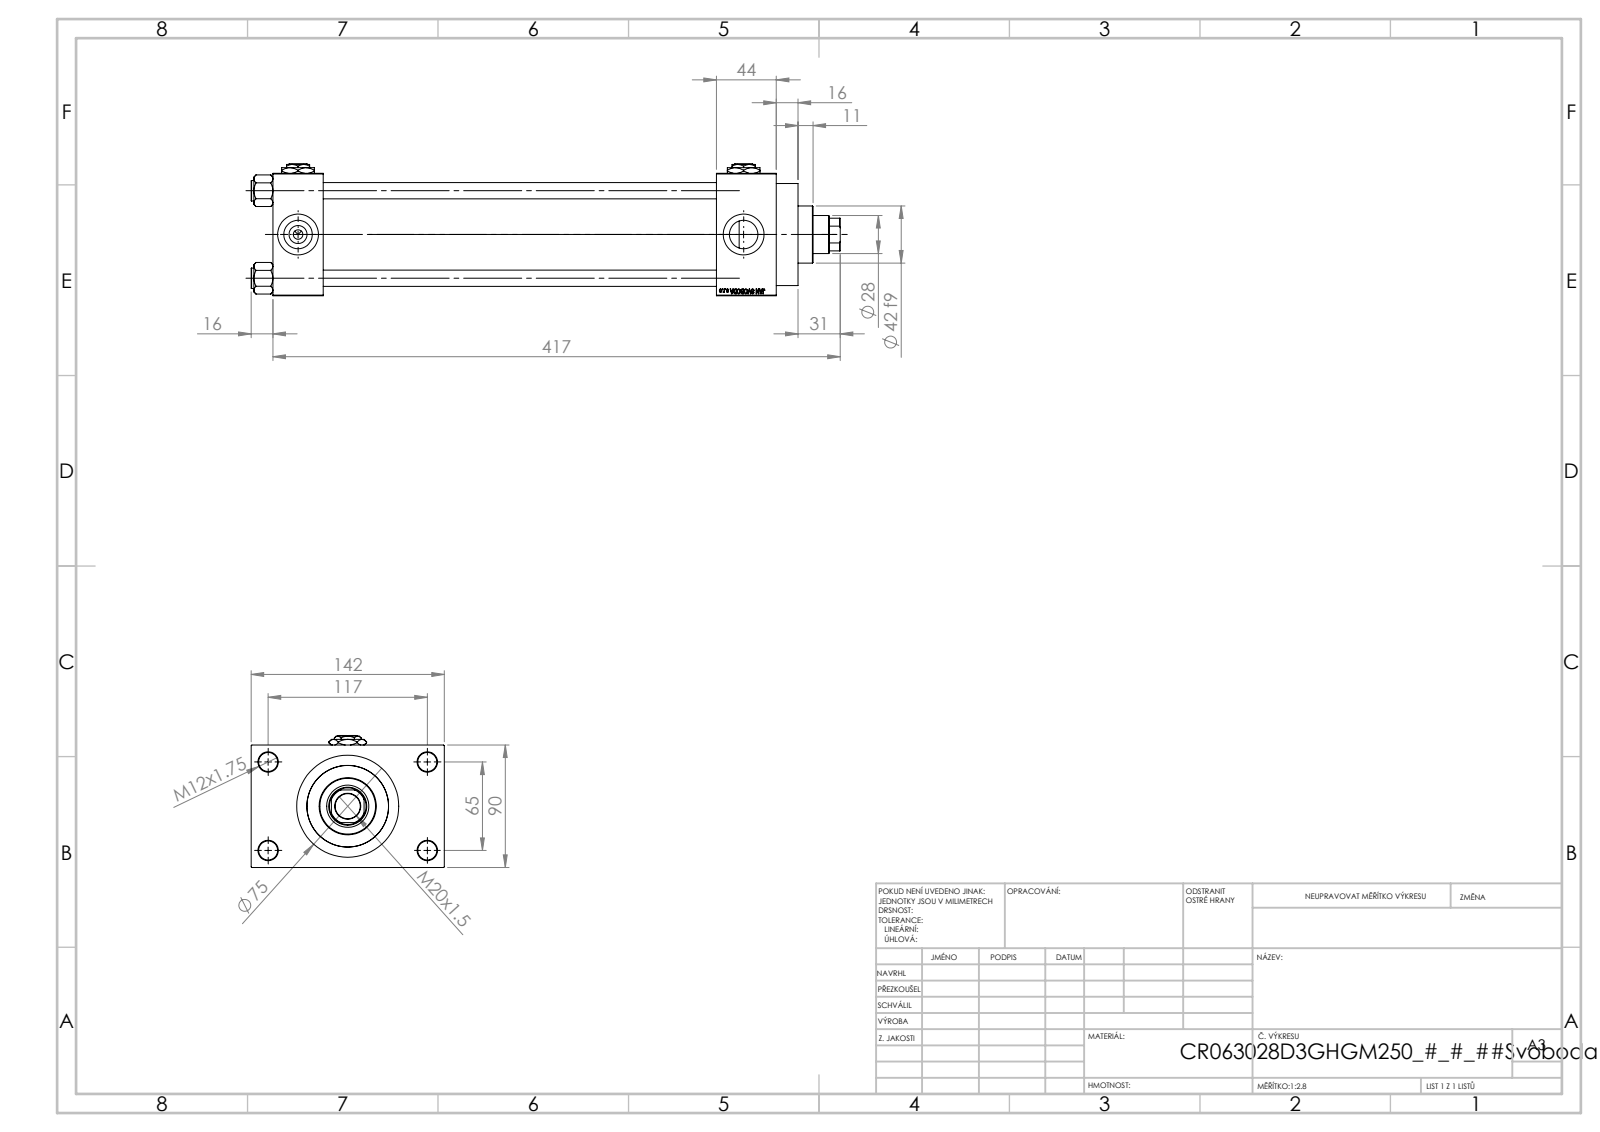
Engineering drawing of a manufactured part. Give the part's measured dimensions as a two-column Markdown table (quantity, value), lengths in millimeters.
| quantity | value |
| --- | --- |
| part name | Zatka_pro_OIL_PORT; V215_VC_A; V215CR_VCP_D; NUT_M5_D (+2 more) |
| STEP written by | SolidWorks 2019 (CONFIG_CONTROL_DESIGN) |
| units | millimeters |
| bodies | 13 solids, 1204 faces (545 planar, 99 cylindrical, 560 other) |
| overall size | 433 × 142 × 97 |
| volume | 1 479 000 mm³ |
| surface area | 355 235 mm² |
| round holes (diameter × count) | 12 × 4, 14 × 4, 20.96 × 4, 30 × 4, 7 × 3, 18.5 × 1, 28 × 1, 31 × 1, 50 × 1, 60 × 1, 63 × 1 |
| round bosses / shafts (diameter × count) | 15 × 4, 75 × 1, 69 × 1, 42 × 1 |
| partial cylindrical surfaces (radius × count) | 13.5 × 1 |
| main face-to-face distances | 90, 289, 37, 326, 333, 370, 44, 26, 116, 16 |
| hole center spacings | 26.35, 45.47, 64.3, 66.92, 69.81, 90.65, 111.34, 65 |
